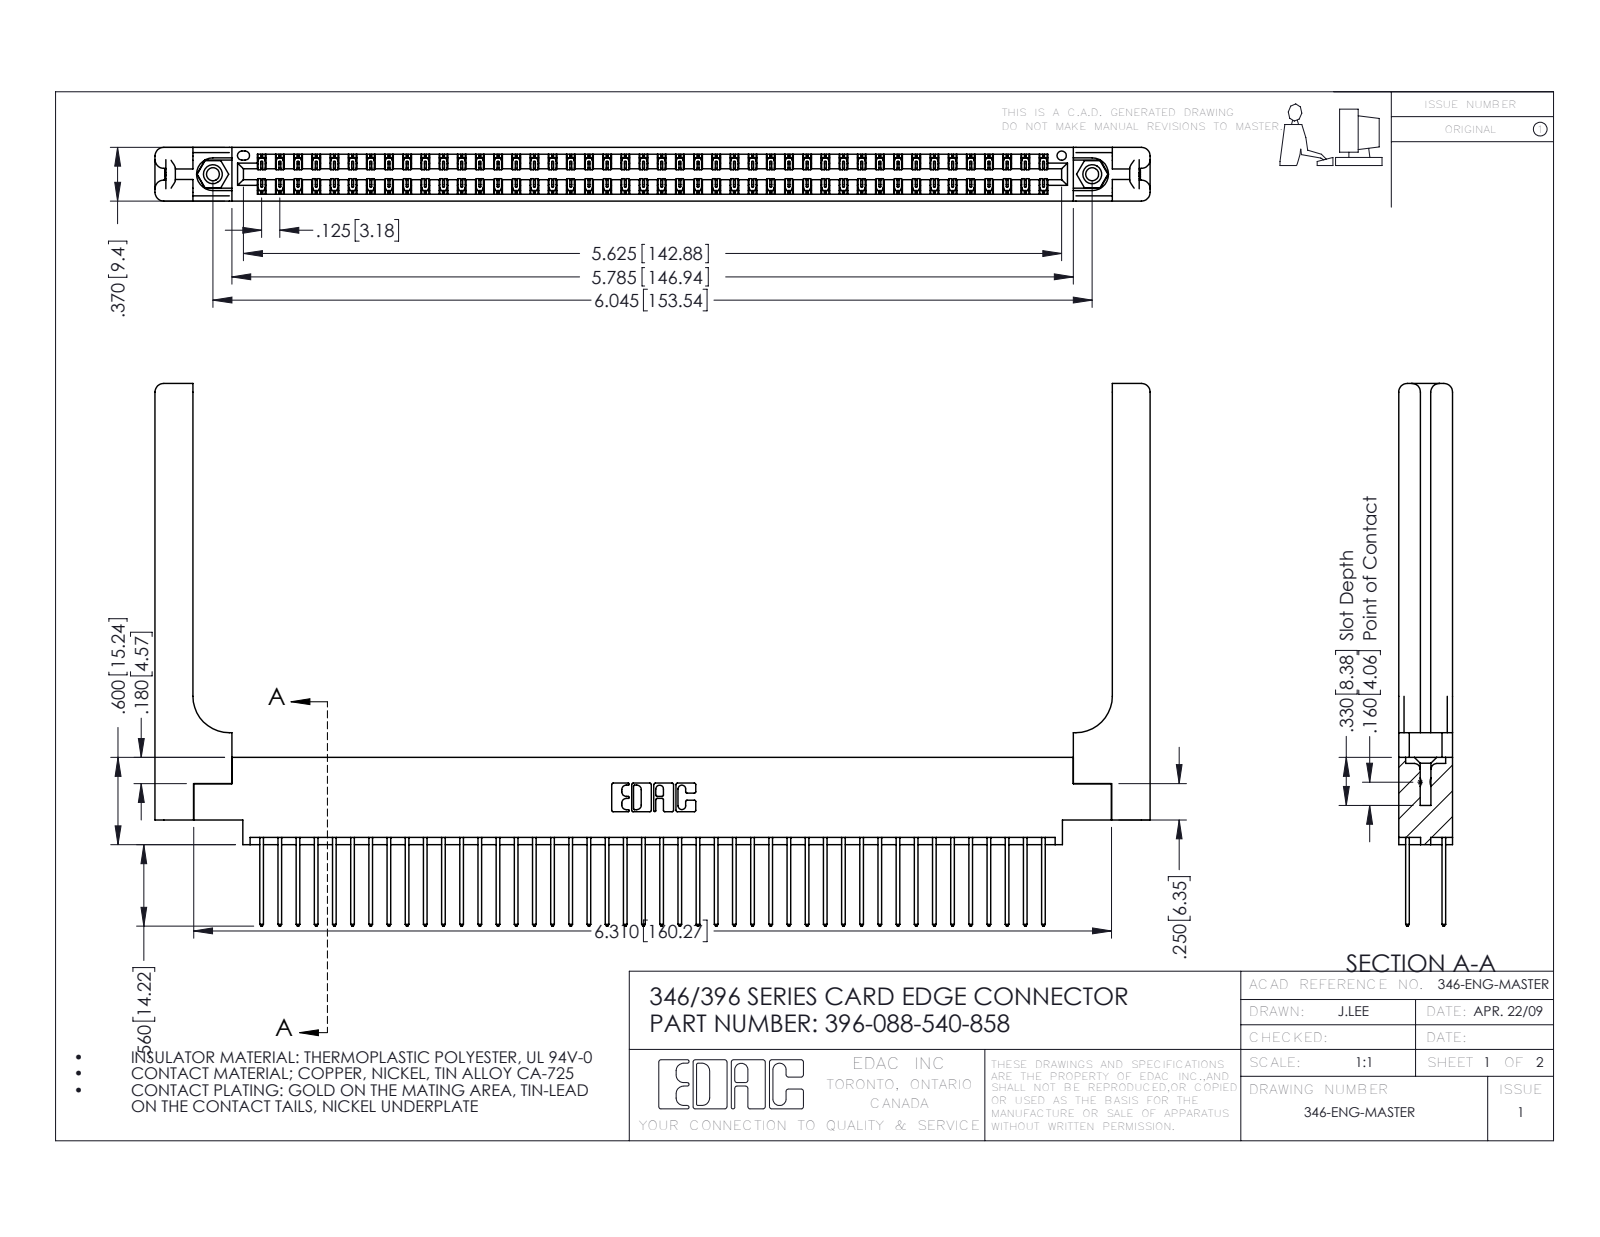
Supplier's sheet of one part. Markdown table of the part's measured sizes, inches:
| quantity | value |
| --- | --- |
| part name | 345-292-001_345-293-140; 396-088-540-858; 345-250-001_345-250-001-102; 346-220-058_345-220-058 (+1 more) |
| STEP written by | SolidWorks 2016 (CONFIG_CONTROL_DESIGN) |
| units | inches |
| bodies | 93 solids, 4958 faces (3308 planar, 1590 cylindrical, 60 other) |
| overall size | 6.841 × 3.73 × 0.37 |
| volume | 1.503 in³ |
| surface area | 47 in² |
| round holes (diameter × count) | 0.089 × 2, 0.125 × 2, 0.156 × 2, 0.064 × 1 |
| round bosses / shafts (diameter × count) | 0.155 × 2 |
| partial cylindrical surfaces (radius × count) | 0.006 × 132, 0.01 × 88, 0.01 × 22, 0.06 × 16, 0.007 × 6, 0.031 × 6, 0.026 × 3, 0.014 × 2 |
| main face-to-face distances | 0.048, 0.322, 0.37, 0.072, 0.25, 0.025, 0.298, 0.148, 0.15, 0.275 |
| hole center spacings | 0.246, 5.836, 6.045 |
